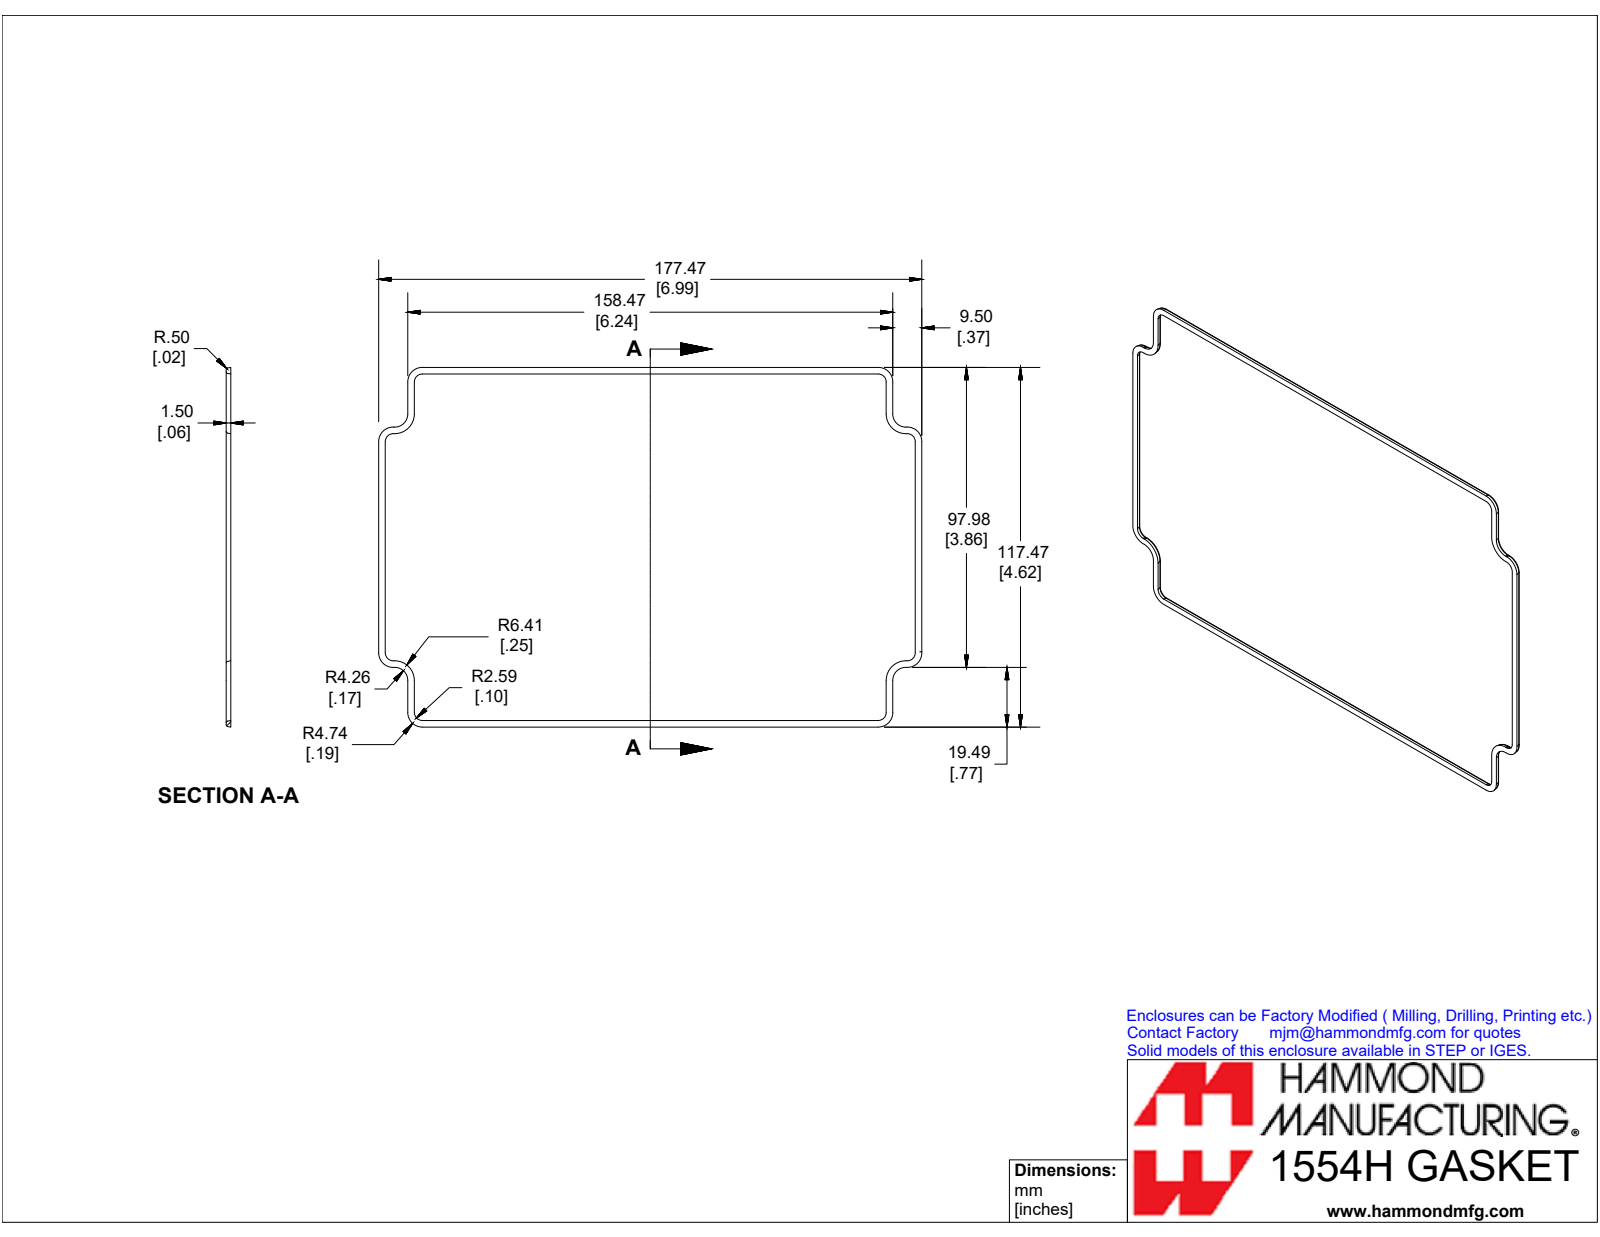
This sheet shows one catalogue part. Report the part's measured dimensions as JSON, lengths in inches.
{"part_name": "1554HGASKET", "step_written_by": "SolidWorks 2019 (CONFIG_CONTROL_DESIGN)", "units": "inches", "bodies": {"solids": 1, "faces": 96, "planar": 25, "cylindrical": 23, "other": 48}, "overall_size": [6.988, 4.625, 0.059], "volume_in3": 0.094, "surface_area_in2": 5.667, "partial_cylinders_radius": [[0.02, 16]], "face_to_face_distances": [0.059, 4.472, 4.472, 6.799, 6.43, 0.369, 0.368, 6.431, 6.062, 6.062]}
